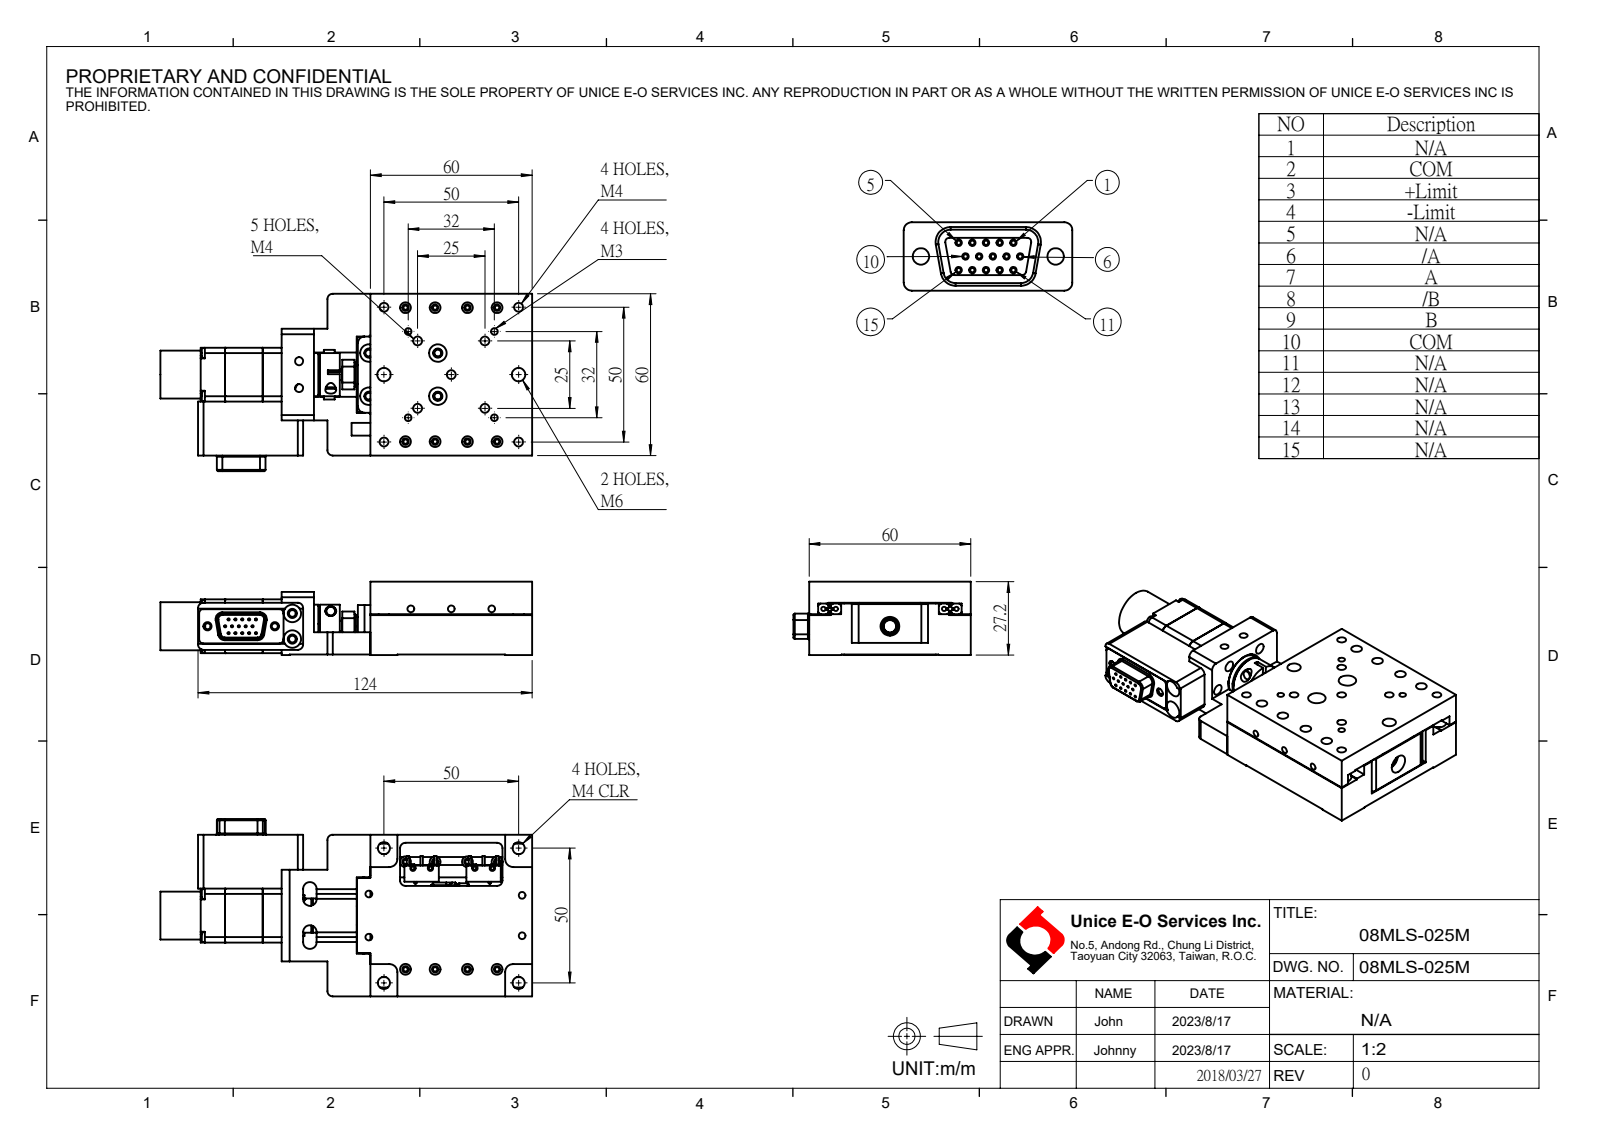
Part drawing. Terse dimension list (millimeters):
name: 08MLS-025M
written by: SolidWorks 2016 (AUTOMOTIVE_DESIGN)
unit: mm
bodies: 0 solids, 585 faces (222 planar, 311 cylindrical, 52 other)
size: 124 × 65.83 × 27.2
holes: 15× ⌀0.8, 13× ⌀2.5, 12× ⌀4, 9× ⌀3.3, 8× ⌀6.5, 6× ⌀7.2, 4× ⌀2, 4× ⌀4.5, 3× ⌀3, 2× ⌀2.26, 2× ⌀2.6, 2× ⌀3.05
bosses: 4× ⌀3.6, 2× ⌀4, 1× ⌀16, 1× ⌀14.8, 1× ⌀8, 1× ⌀6.2, 1× ⌀5.4, 1× ⌀5
rounds: 22× R2, 9× R2.5, 8× R0.5, 4× R1, 4× R1.5, 4× R3, 2× R1.8, 1× R4.75
face distances: 27, 19.2, 7.8, 60, 4.3, 4, 15.85, 44.15, 20, 18.9
hole spacings: 2.84, 4.58, 5.08, 25, 2.54, 6.84, 17.68, 39.53
